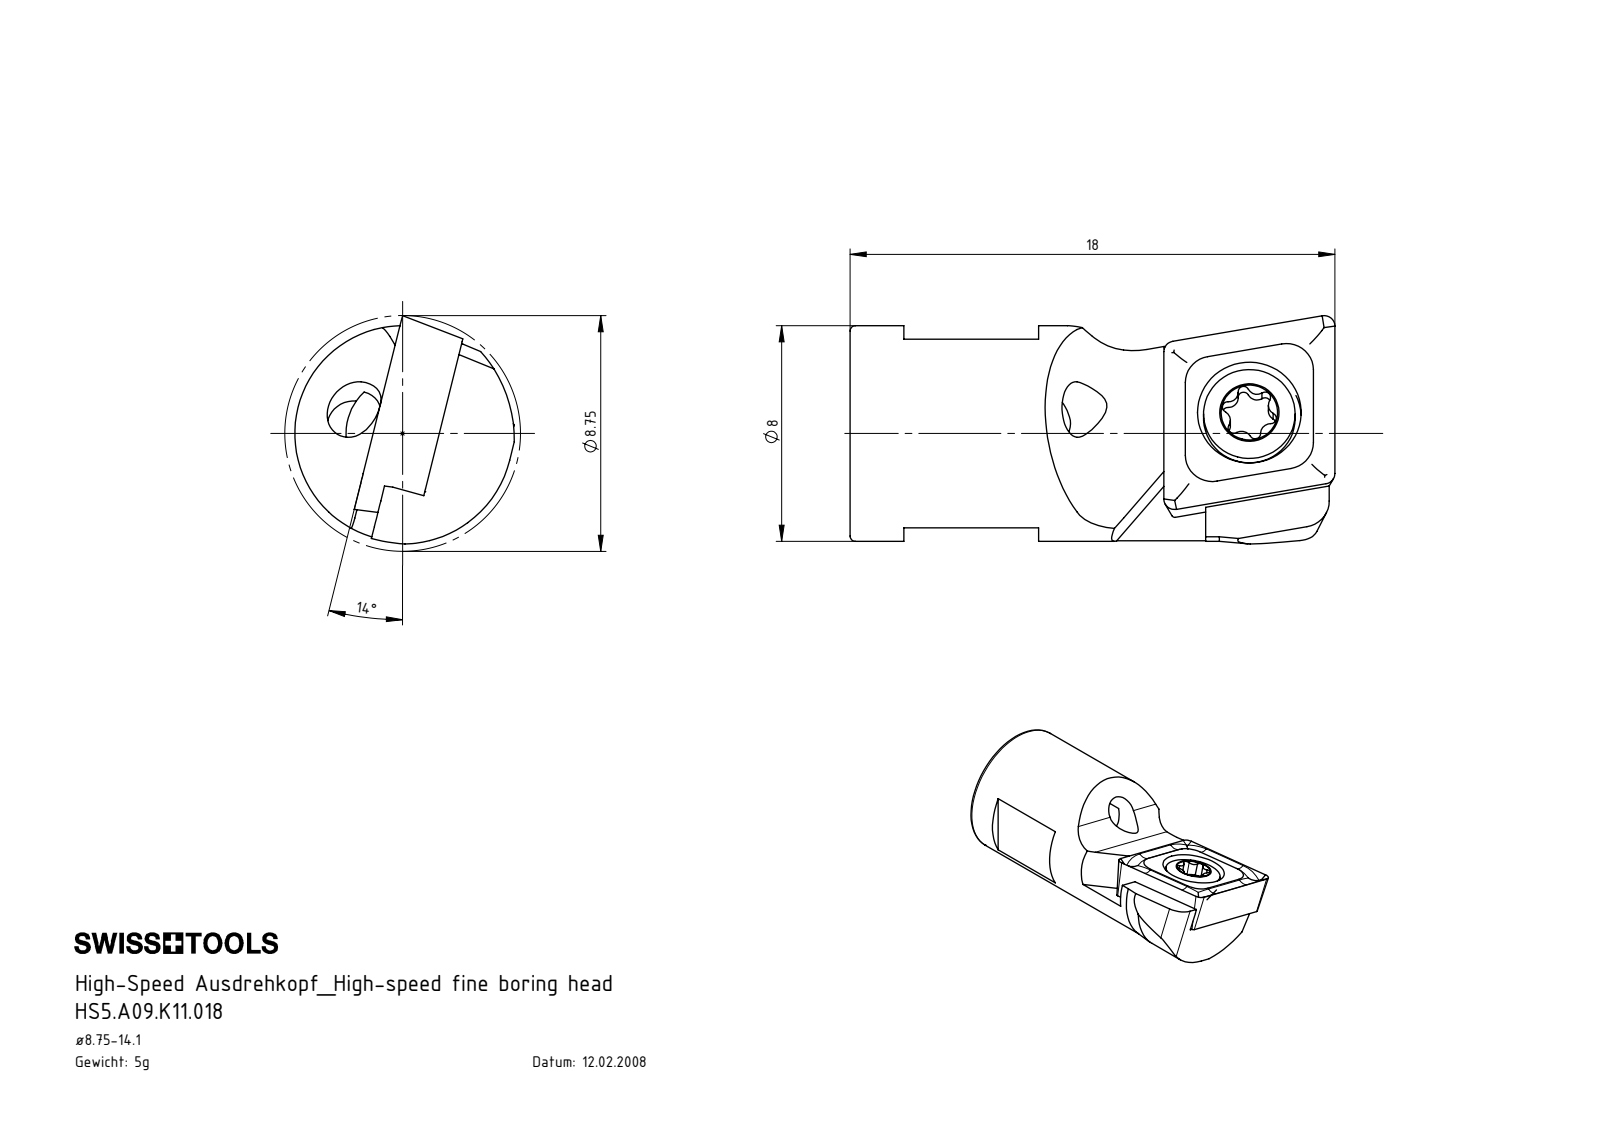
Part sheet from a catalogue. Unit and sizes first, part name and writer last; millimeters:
Units: millimetres
Overall size (bounding box): 18 × 8.47 × 8.15
Round holes (diameter × count): ⌀2 ×1, ⌀2.05 ×1, ⌀2.8 ×1, ⌀3.85 ×1, ⌀4.2 ×1
Round bosses / shafts (diameter × count): ⌀8 ×1, ⌀3.4 ×1, ⌀2.5 ×1
Partial cylindrical surfaces — rounded edges, fillets, slot ends (radius × count): R0.21 ×6, R0.36 ×5, R0.36 ×1, R1 ×1, R2 ×1, R3 ×1, R4.1 ×1, R4.9 ×1
Main face-to-face distances: 7, 2.38, 2.28, 1.5, 0.78, 0.88, 11.8, 5, 4.8, 2
Volume: 564 mm³ · Surface area: 796 mm²
Bodies: 3 solids, 129 faces (40 planar, 38 cylindrical, 51 other)
Part name (STEP PRODUCT): WCA-ER2.001.005_A; HS5.A09.K11.018; CCMT060204; HS5-A09.K11.018_D
STEP written by: SolidWorks 2017 (AUTOMOTIVE_DESIGN)
